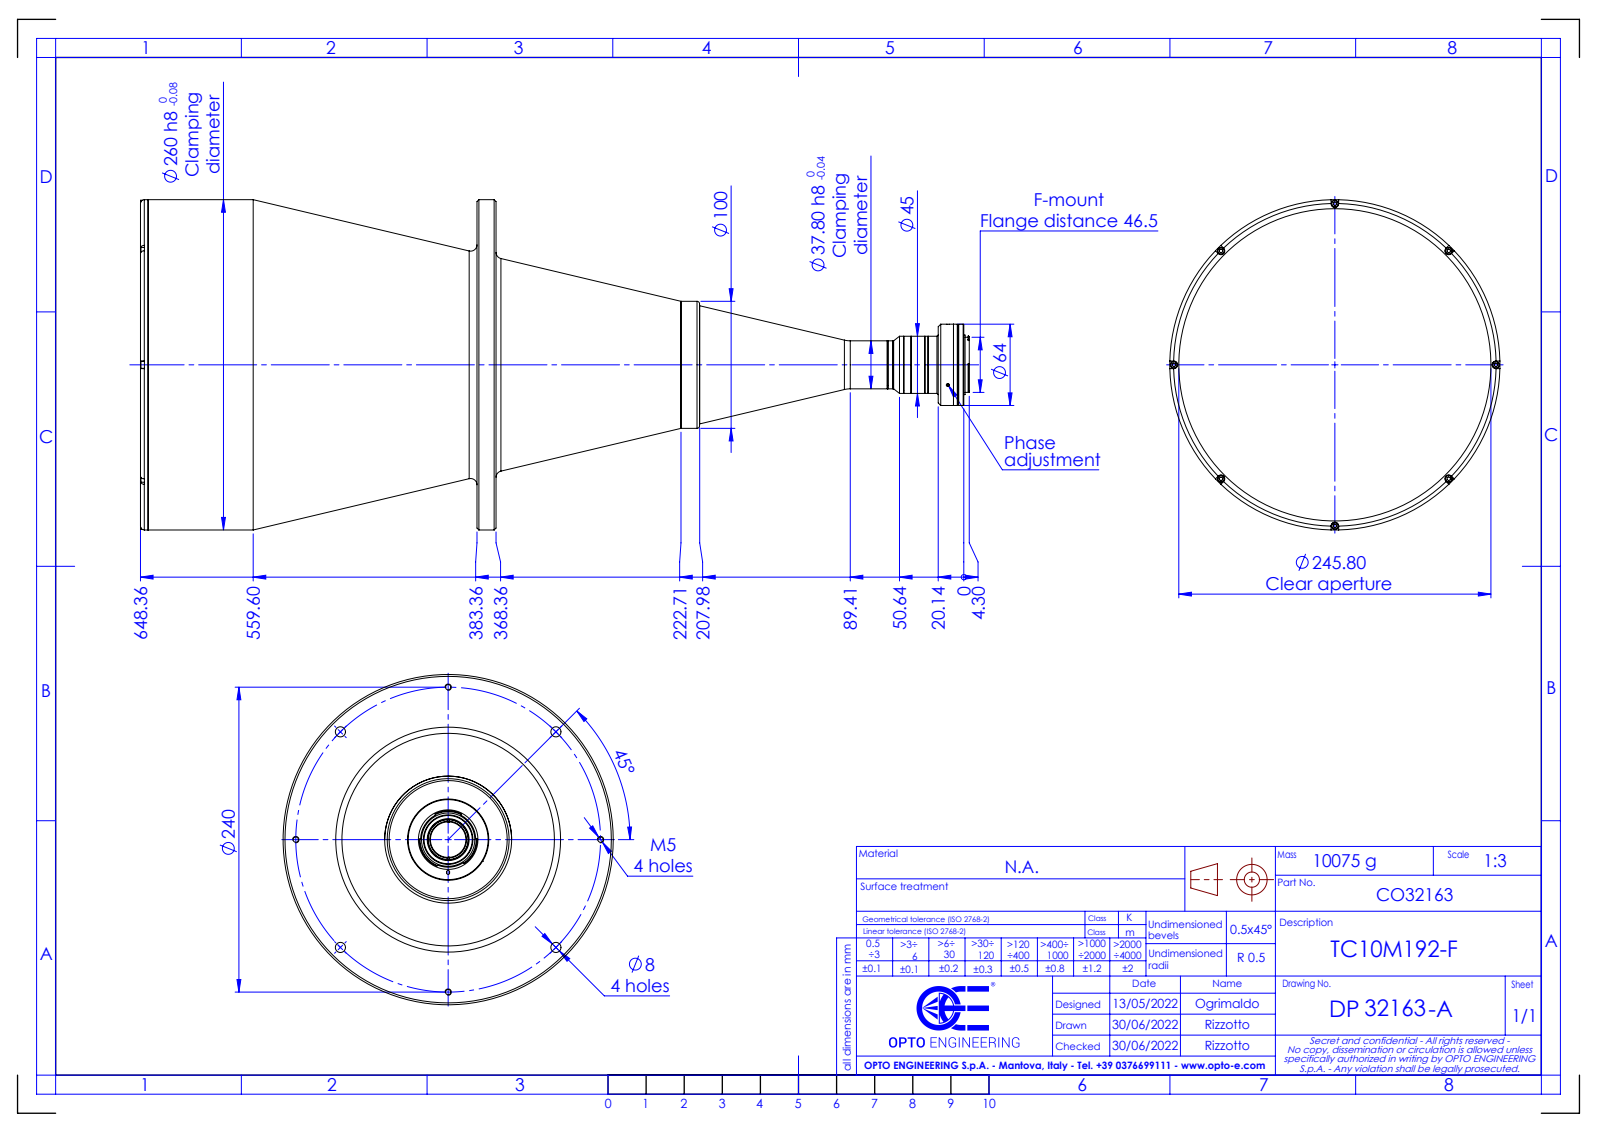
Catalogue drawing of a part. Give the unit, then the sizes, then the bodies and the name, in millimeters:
Units: millimetres
Overall size (bounding box): 652.66 × 260 × 260
Round holes (diameter × count): ⌀4.2 ×4, ⌀8 ×4, ⌀2.5 ×1, ⌀33 ×1, ⌀42 ×1, ⌀245.8 ×1, ⌀255 ×1
Round bosses / shafts (diameter × count): ⌀5.5 ×8, ⌀260 ×1, ⌀100 ×1, ⌀93 ×1, ⌀64 ×1, ⌀63.5 ×1, ⌀46.9 ×1, ⌀45 ×1
Partial cylindrical surfaces — rounded edges, fillets, slot ends (radius × count): R3 ×4, R1.15 ×2, R22.65 ×1
Main face-to-face distances: 15, 265, 280, 18, 247, 262, 629.71, 611.71, 364.71, 349.71
Hole centre spacings: 91.84, 120, 221.73, 169.7, 169.71, 239.99, 240
Bodies: 0 solids, 208 faces (55 planar, 97 cylindrical, 56 other)
Part name (STEP PRODUCT): DP32163-A_TC10M192-F
STEP written by: SolidWorks 2021 (CONFIG_CONTROL_DESIGN)
